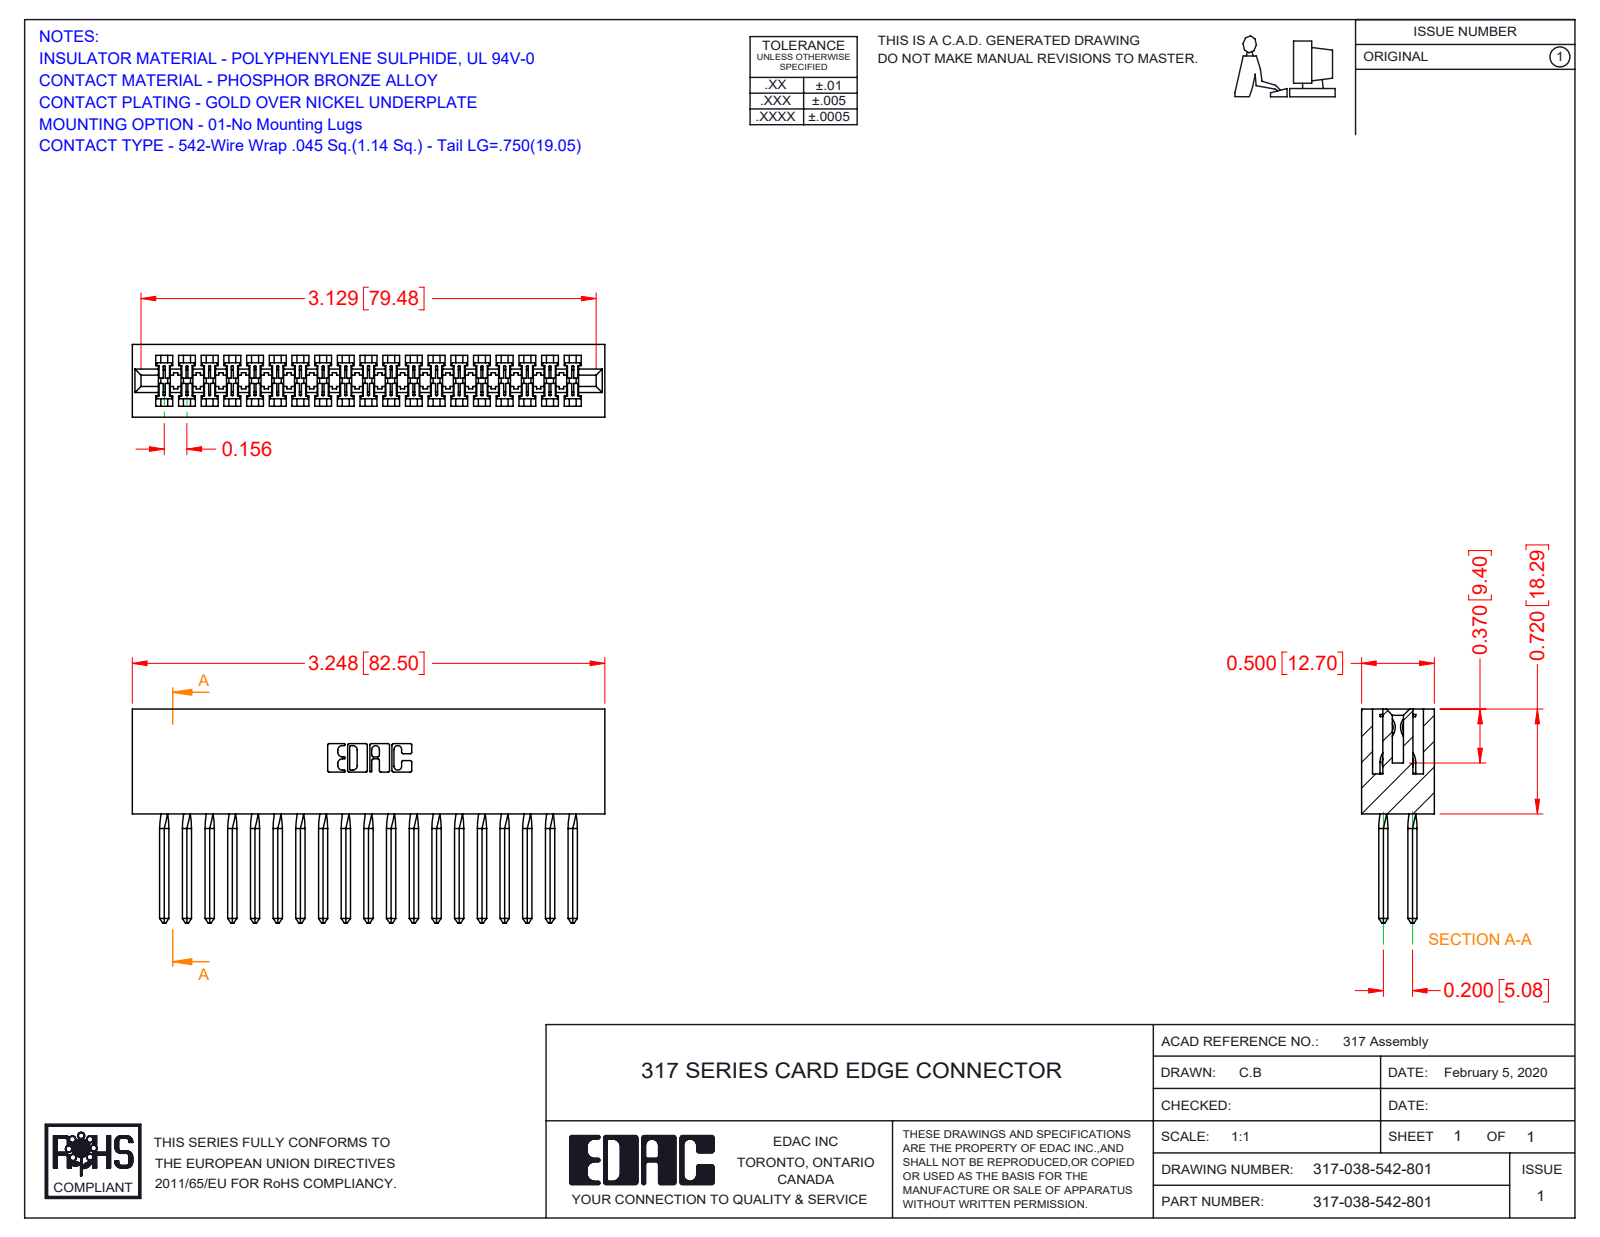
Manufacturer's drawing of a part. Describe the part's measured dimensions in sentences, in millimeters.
The part is named "317-038-542-801; 317-290-003_542; 317 Part_Lugless". Its 3-D file was written by "SolidWorks 2016 (CONFIG_CONTROL_DESIGN)". It is 39 solids with 2256 faces: 1798 planar, 306 cylindrical and 152 other. Overall it measures 82.5 by 37.3 by 12.7 millimeters. Its volume is 14 500 cubic millimeters and its surface area 19 620 square millimeters. Partial cylindrical surfaces (rounded edges, fillets, slot ends): 76 of radius 0.2, 22 of radius 0.3, 6 of radius 0.2, 6 of radius 0.8, 3 of radius 0.7, 2 of radius 1.9, 2 of radius 2.3, 2 of radius 2.5. The main face-to-face distances are 12.7, 1.9, 10.8, 2.8, 8.9, 2.9, 5.1, 3.5, 18.3, 1.2.
